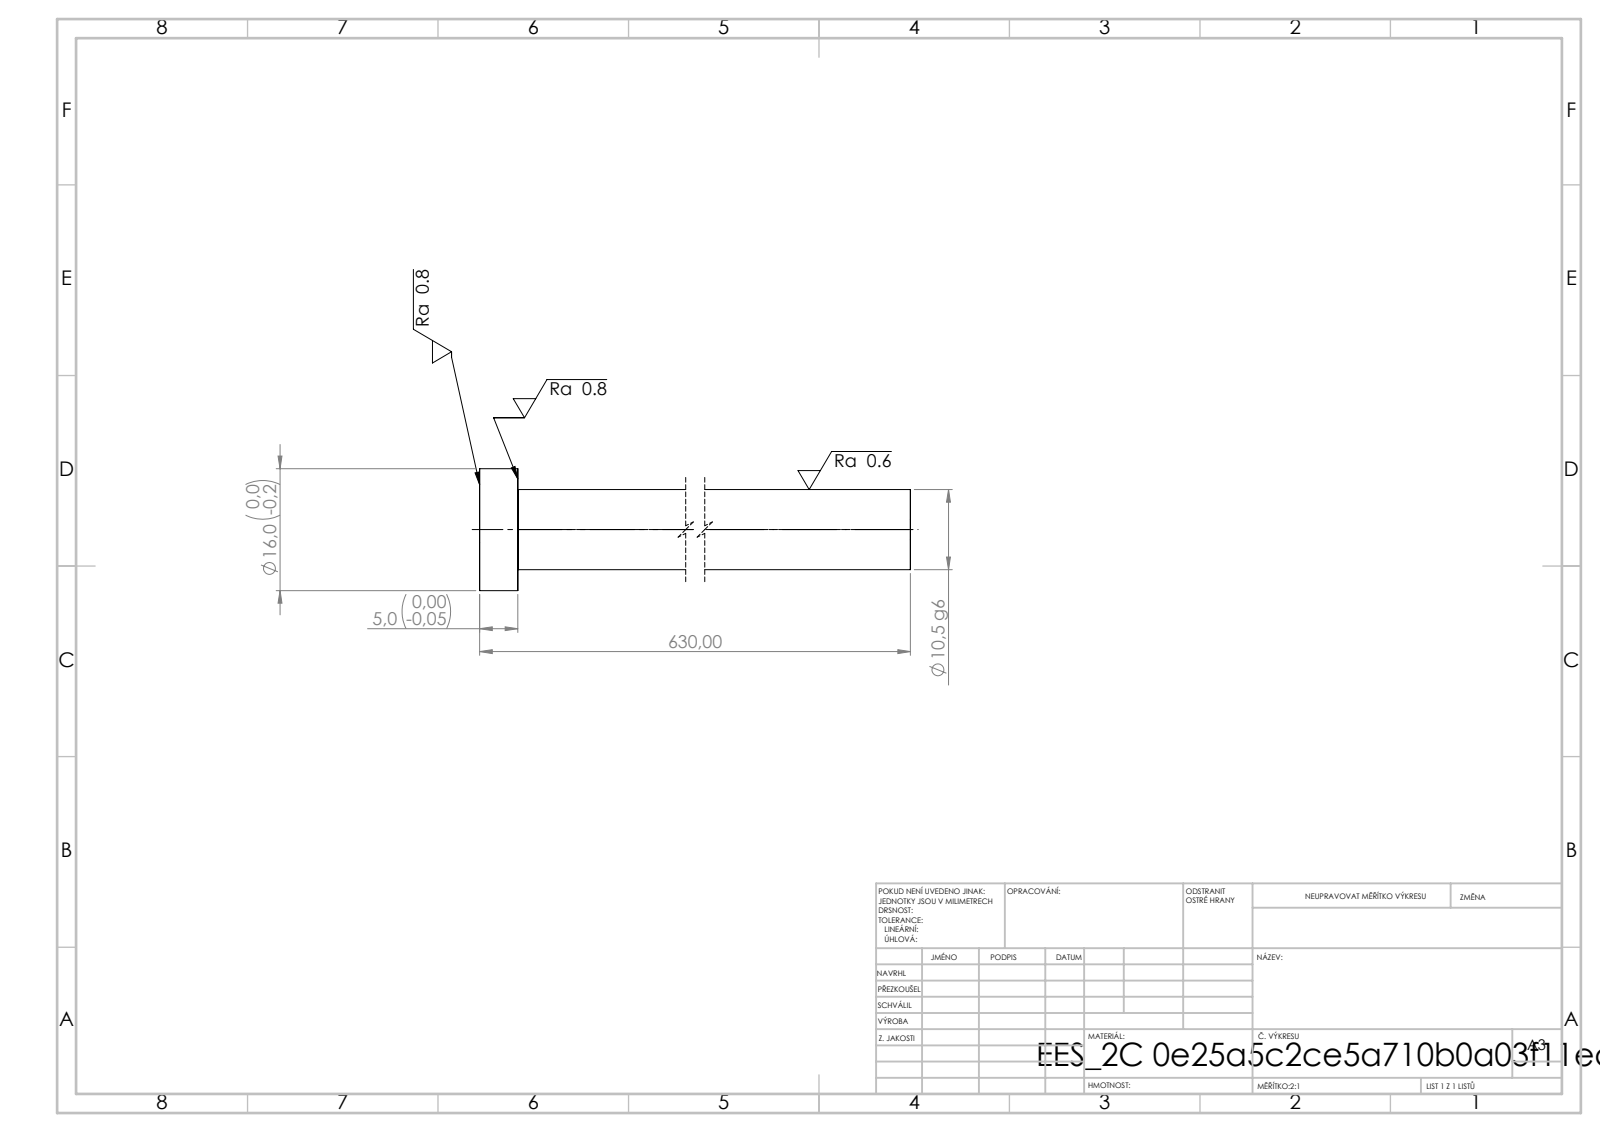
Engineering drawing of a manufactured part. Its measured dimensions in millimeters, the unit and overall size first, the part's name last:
Units: millimetres
Overall size (bounding box): 630 × 16 × 16
Round bosses / shafts (diameter × count): ⌀16 ×1, ⌀10.5 ×1
Main face-to-face distances: 5, 630, 625
Volume: 55 124 mm³ · Surface area: 21 270 mm²
Bodies: 1 solid, 7 faces (3 planar, 4 cylindrical, 0 other)
STEP written by: SolidWorks 2019 (CONFIG_CONTROL_DESIGN)
